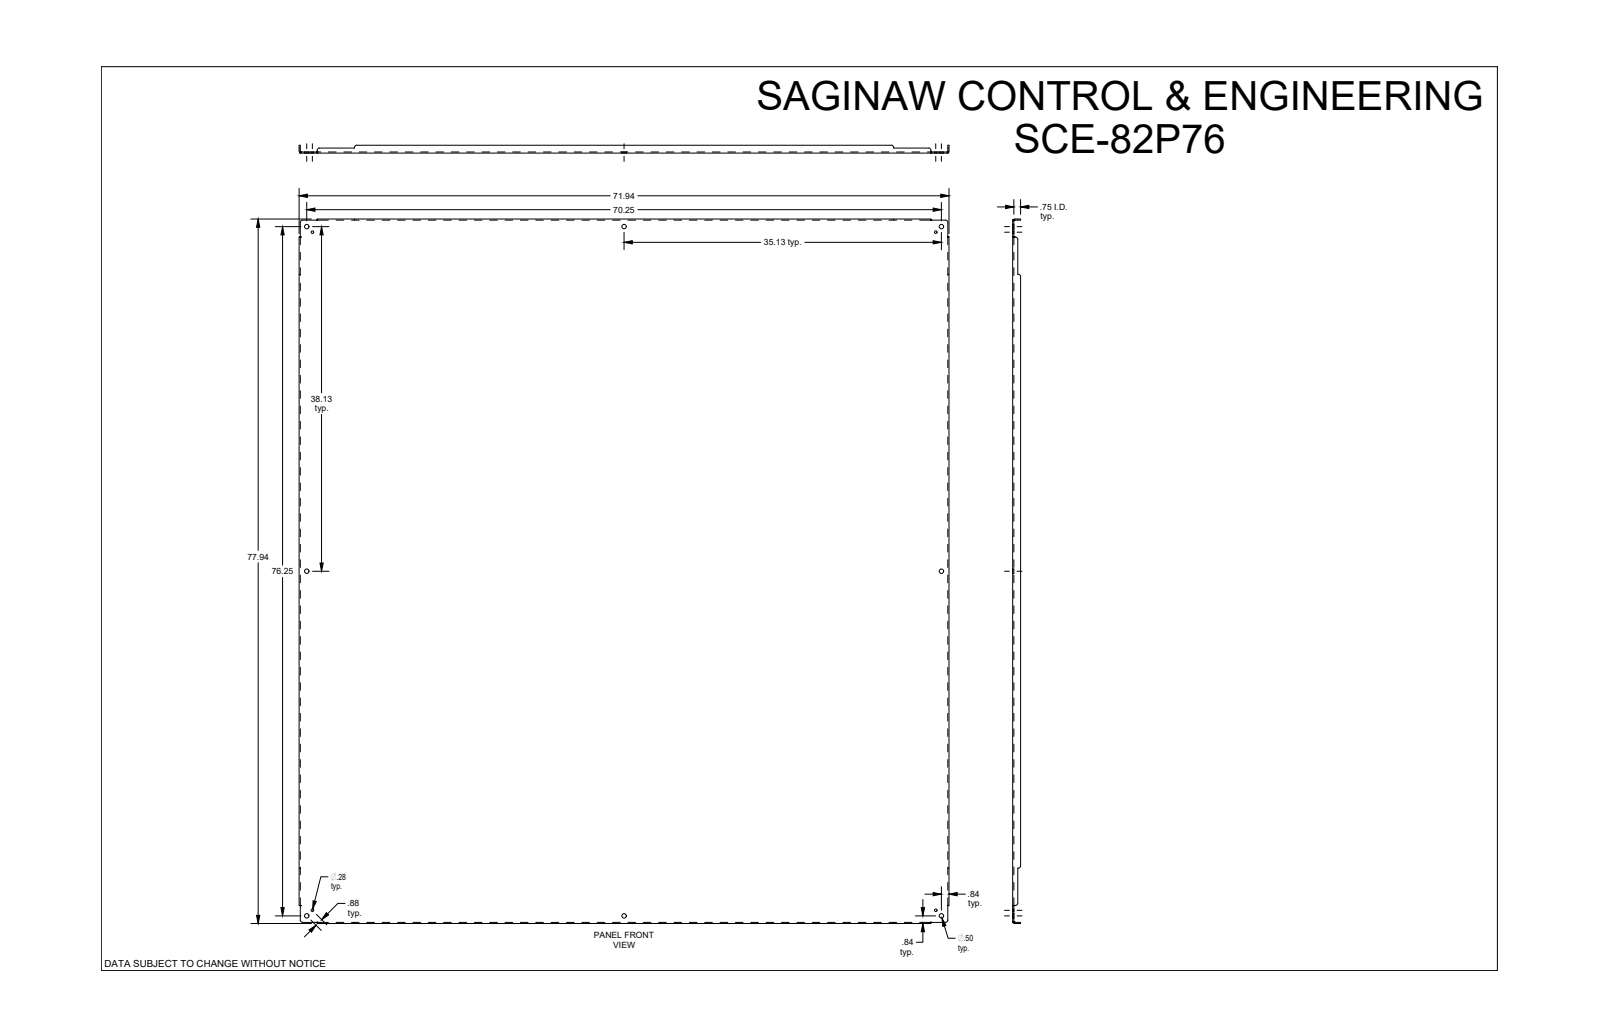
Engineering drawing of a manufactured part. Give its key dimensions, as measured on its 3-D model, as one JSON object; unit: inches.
{"part_name": "SCE-82P76", "step_written_by": "SolidWorks 2019 (CONFIG_CONTROL_DESIGN)", "units": "inches", "bodies": {"solids": 1, "faces": 110, "planar": 46, "cylindrical": 40, "other": 24}, "overall_size": [77.938, 71.938, 0.875], "volume_in3": 723, "surface_area_in2": 11608, "round_holes": [[0.5, 8], [0.281, 4]], "partial_cylinders_radius": [[0.25, 12], [0.112, 4], [0.237, 4]], "face_to_face_distances": [0.125, 0.125, 71.813, 77.813, 71.687, 71.938, 77.687, 77.938, 0.75, 0.875], "hole_center_spacings": [0.875, 34.512, 35.125, 37.511, 38.125, 51.839, 69.634, 75.634]}
